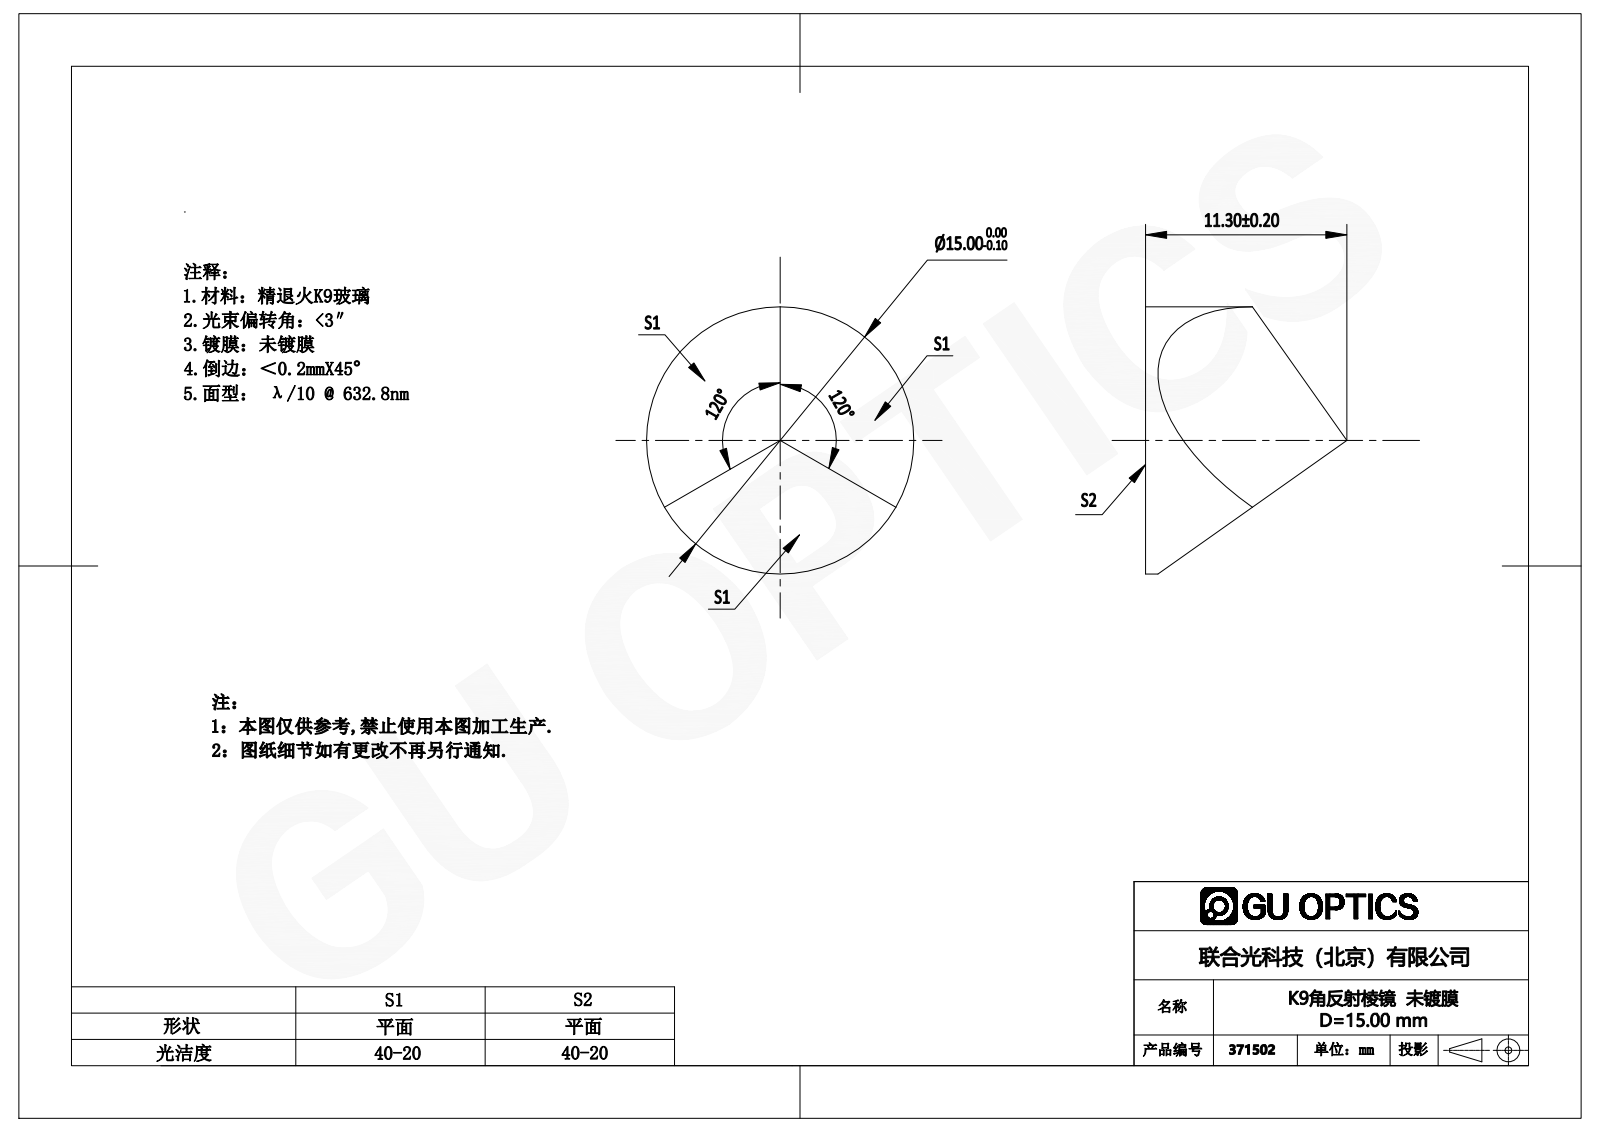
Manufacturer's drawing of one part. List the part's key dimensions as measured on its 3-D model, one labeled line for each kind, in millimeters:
Part name (STEP PRODUCT): 371502
STEP written by: SolidWorks 2016 (CONFIG_CONTROL_DESIGN)
Units: millimetres
Bodies: 1 solid, 6 faces (4 planar, 2 cylindrical, 0 other)
Overall size (bounding box): 15 × 15 × 11.3
Volume: 964 mm³ · Surface area: 602 mm²
Round bosses / shafts (diameter × count): ⌀15 ×1
